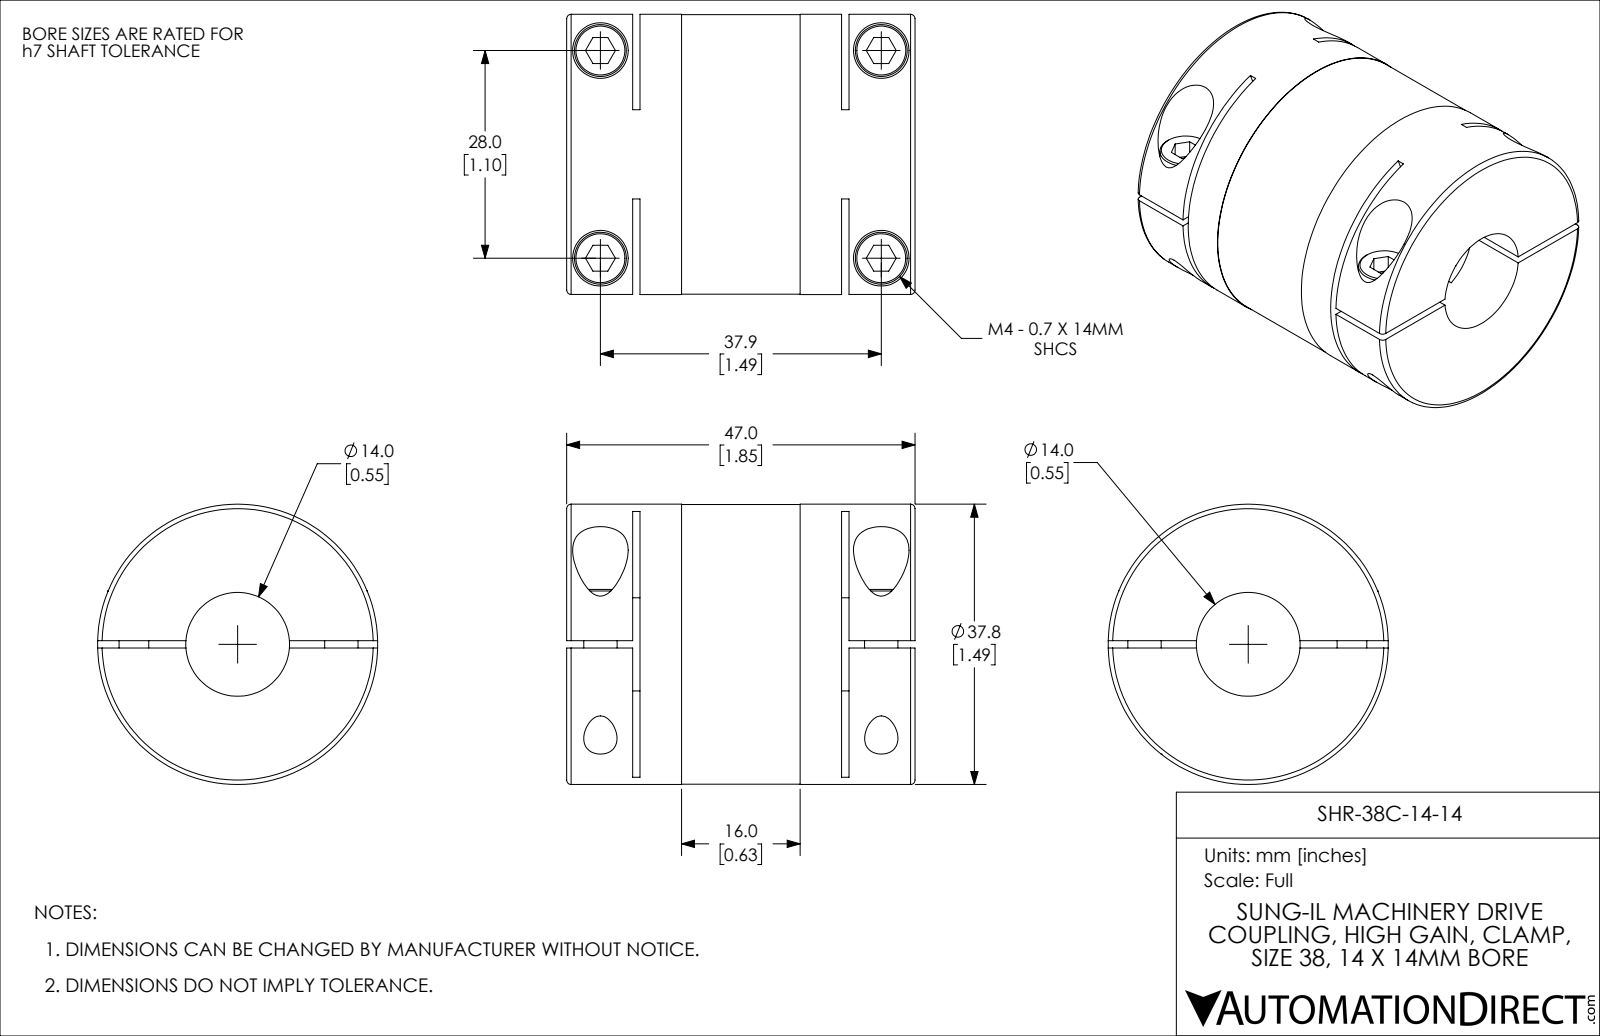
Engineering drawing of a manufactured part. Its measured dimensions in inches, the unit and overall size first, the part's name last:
Units: inches
Overall size (bounding box): 1.85 × 1.488 × 1.488
Round holes (diameter × count): ⌀0.177 ×4, ⌀0.295 ×4, ⌀0.551 ×1, ⌀0.63 ×1
Round bosses / shafts (diameter × count): ⌀0.276 ×4, ⌀0.157 ×2, ⌀1.488 ×1, ⌀1.484 ×1
Partial cylindrical surfaces — rounded edges, fillets, slot ends (radius × count): R1.969 ×2
Main face-to-face distances: 0.039, 0.39, 1.461, 0.35, 1.5, 1.11, 1.85, 1.071, 1.15, 1.24
Hole centre spacings: 1.102, 1.492, 1.855
Volume: 2.527 in³ · Surface area: 23.47 in²
Bodies: 1 solid, 144 faces (70 planar, 58 cylindrical, 16 other)
Part name (STEP PRODUCT): SHR-38C-14-14
STEP written by: SolidWorks 2021 (CONFIG_CONTROL_DESIGN)
